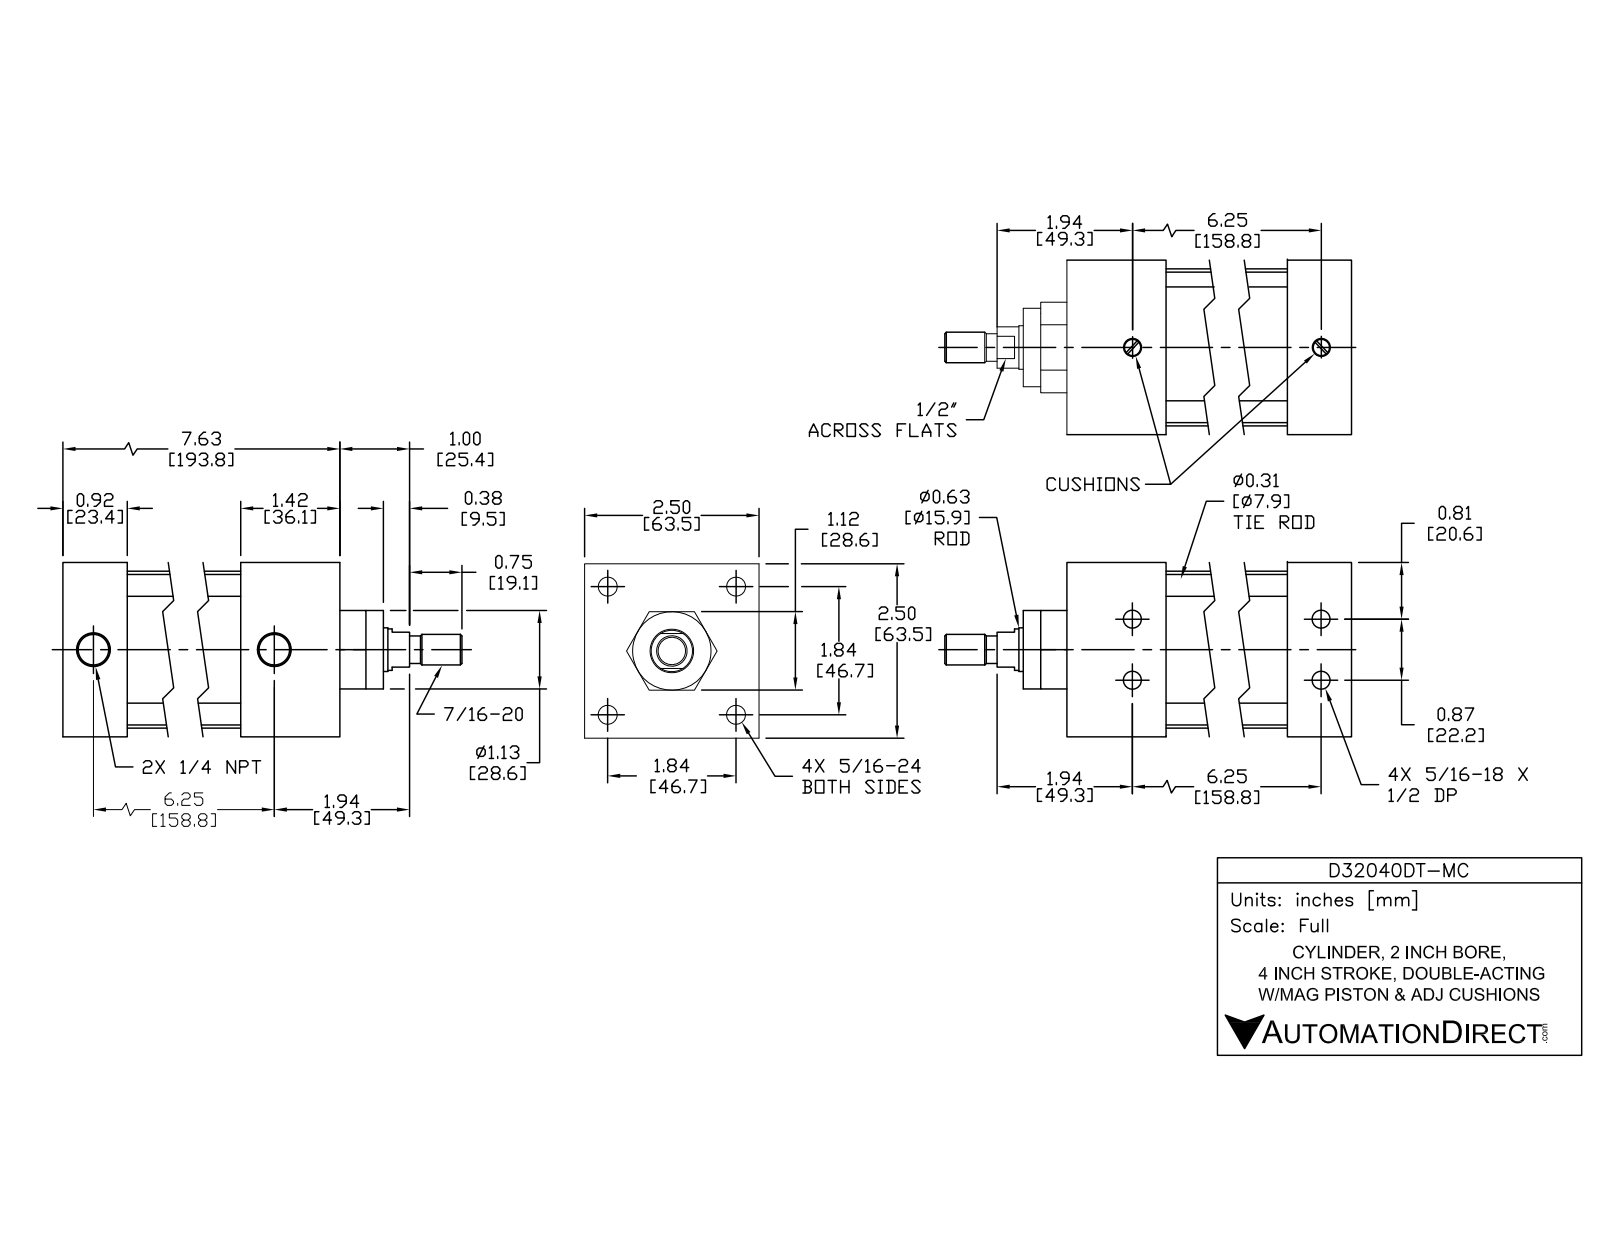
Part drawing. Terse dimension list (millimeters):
name: D32040DT-MC; D32040DT-M PISTON; D32040DT-M BODY
written by: SolidWorks 2015 (AUTOMOTIVE_DESIGN)
unit: mm
bodies: 12 solids, 298 faces (94 planar, 114 cylindrical, 90 other)
size: 238 × 63.5 × 63.5
volume: 416 100 mm³; area: 128 300 mm²
holes: 4× ⌀6.4, 4× ⌀6.8, 4× ⌀9.1, 4× ⌀12.7, 2× ⌀7.5, 2× ⌀12.1, 1× ⌀15.9, 1× ⌀16, 1× ⌀50.8
bosses: 4× ⌀12.3, 4× ⌀8, 4× ⌀7.2, 1× ⌀57.2, 1× ⌀50.7, 1× ⌀28.4, 1× ⌀15.8, 1× ⌀15
rounds: 4× R6.4
face distances: 63.5, 193.6, 36.1, 157.5, 170.2, 134.1, 23.4, 25.4, 167.7, 131.6
hole spacings: 33.2, 46.9, 159, 158.6, 11.1, 11.1, 22.2, 66.4
